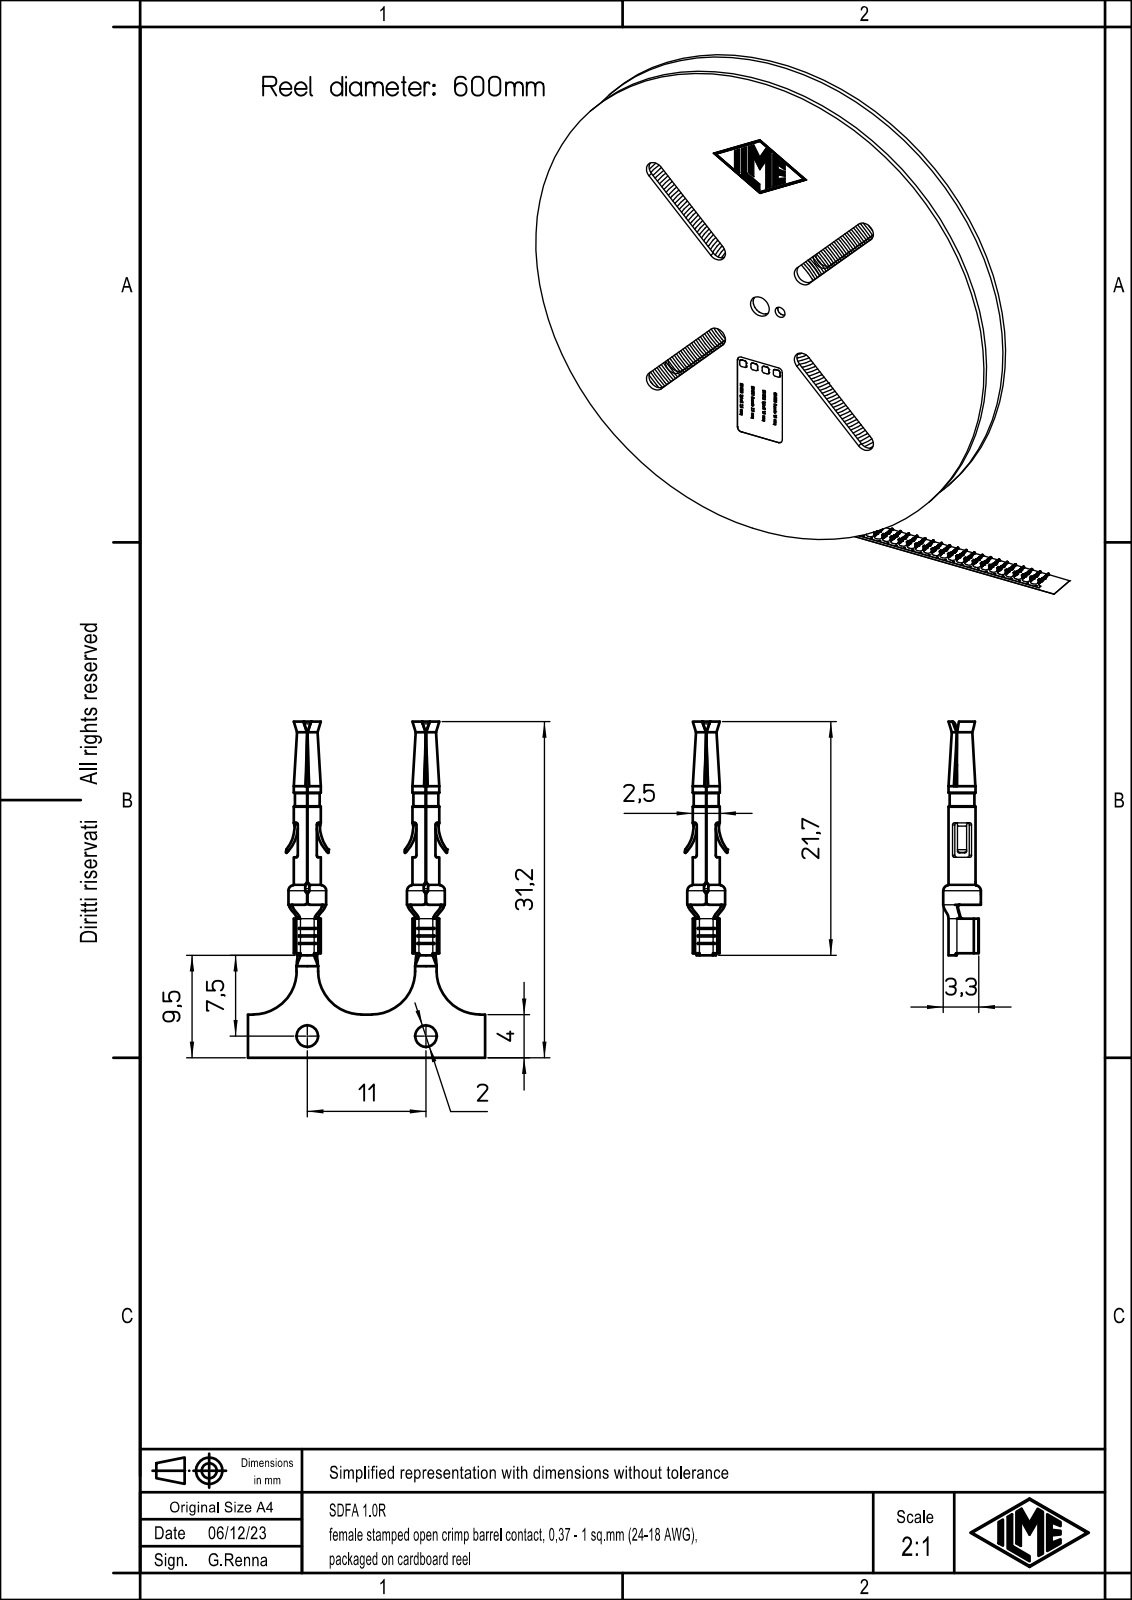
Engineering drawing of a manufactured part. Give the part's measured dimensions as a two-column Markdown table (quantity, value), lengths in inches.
| quantity | value |
| --- | --- |
| part name | SDFA_1.0 |
| STEP written by | Creo Elements/Direct Modeling 20.1B 02-Apr-2019 (C) Parametric Technology GmbH (AUTOMOTIVE_DESIGN) |
| units | inches |
| bodies | 1 solid, 214 faces (68 planar, 83 cylindrical, 63 other) |
| overall size | 0.854 × 0.156 × 0.138 |
| volume | 0.002 in³ |
| surface area | 0.471 in² |
| round holes (diameter × count) | 0.067 × 1, 0.075 × 1, 0.114 × 1 |
| round bosses / shafts (diameter × count) | 0.138 × 1, 0.098 × 1, 0.091 × 1 |
| partial cylindrical surfaces (radius × count) | 0.008 × 26, 0.138 × 4, 0.004 × 2, 0.026 × 1, 0.03 × 1, 0.037 × 1 |
| main face-to-face distances | 0.033, 0.177, 0.126, 0.051, 0.35, 0.224, 0.173, 0.134, 0.185, 0.358 |
